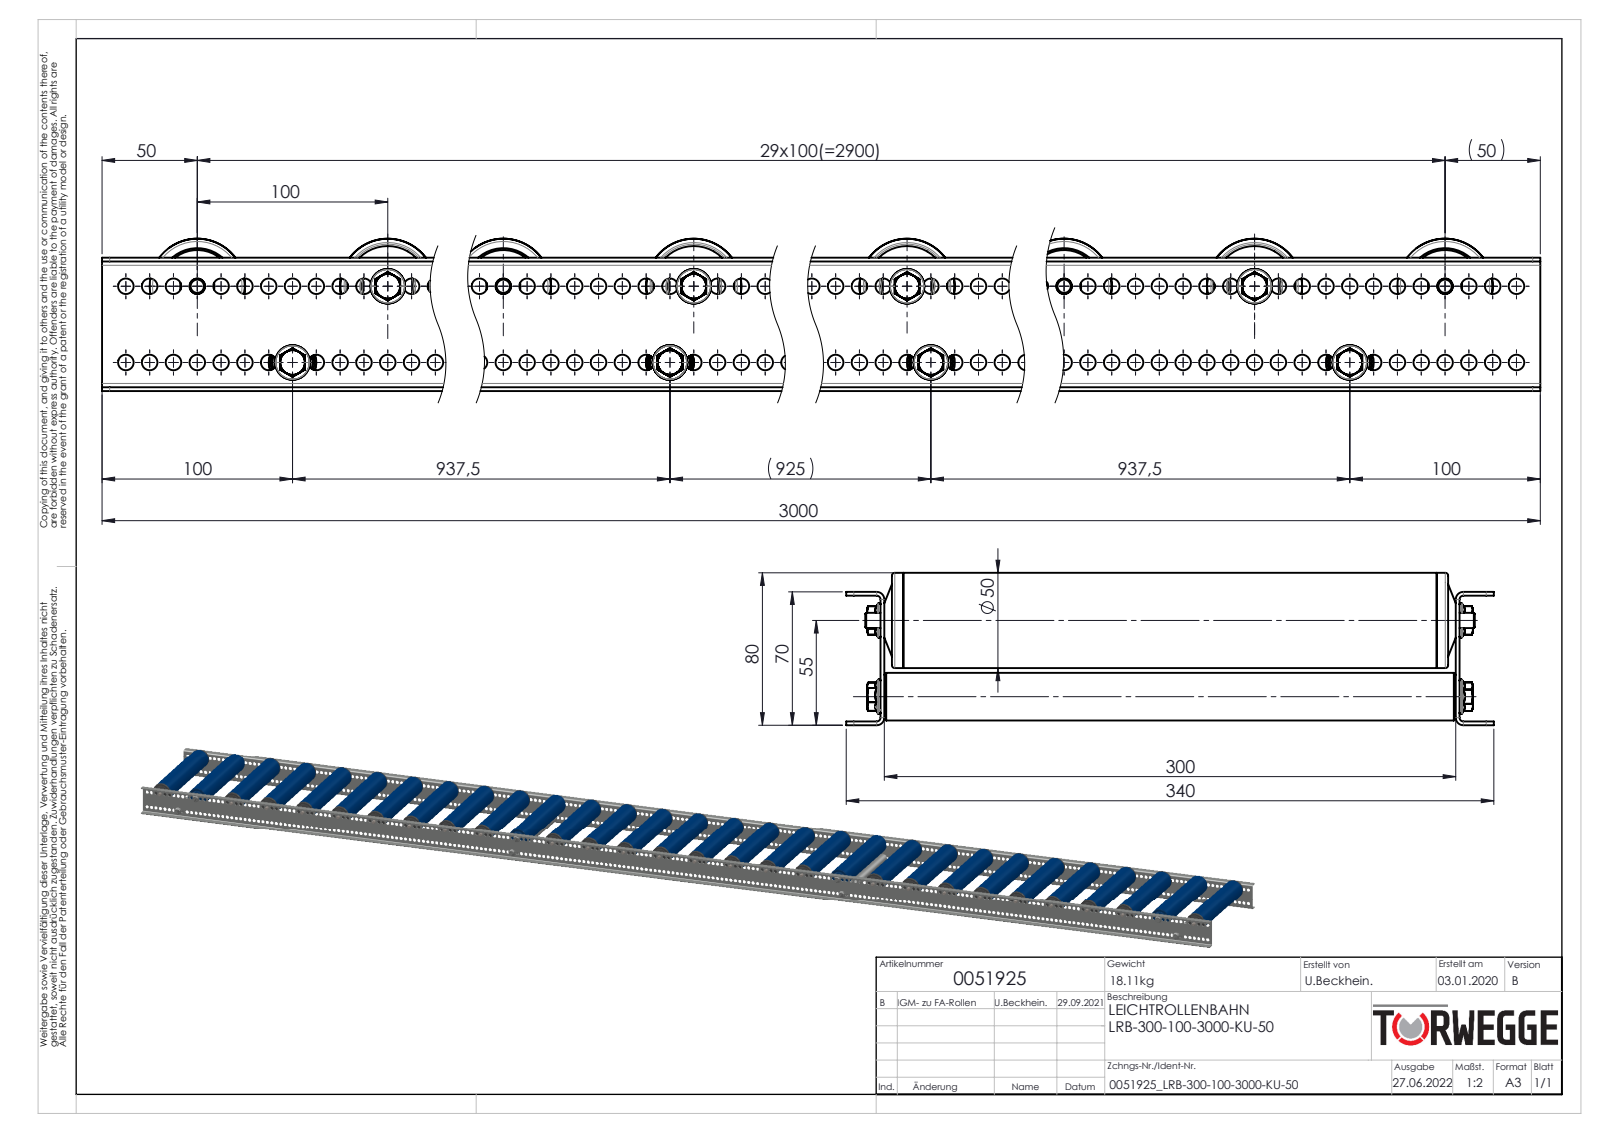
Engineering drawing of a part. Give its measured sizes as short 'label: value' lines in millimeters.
name: KUT100-50x2,8-KB-A12-IGM8-EL=KFG_S100913_KUT100-50x2,8-KB-A12-IGM8-EL=300; 0039778-Achse-ST-Ø08-KFG_AL320-G; Druckfeder_1,2x10x30; Sicherungsring_DIN471_8x0.8_Circlip DIN 471 - 8 x 0.8 (+8 more)
written by: SolidWorks 2020 (AUTOMOTIVE_DESIGN)
unit: mm
bodies: 529 solids, 10474 faces (2574 planar, 4860 cylindrical, 3040 other)
size: 3000 × 340 × 80
volume: 7 085 000 mm³; area: 5 481 000 mm²
holes: 478× ⌀8.2, 26× ⌀7.6, 26× ⌀8, 26× ⌀25, 26× ⌀30, 26× ⌀35, 26× ⌀39.4, 26× ⌀40, 8× ⌀6.8, 4× ⌀12, 4× ⌀12.1, 4× ⌀16
bosses: 30× ⌀50, 26× ⌀44.4, 26× ⌀38, 26× ⌀36, 26× ⌀33, 26× ⌀22, 26× ⌀21, 8× ⌀25
rounds: 52× R0.6, 52× R0.75, 52× R2.45, 26× R4.87, 26× R7, 16× R2.5, 8× R4, 4× R2
face distances: 2, 302, 68, 300, 304, 70, 66, 292, 6, 12
hole spacings: 12.5, 25, 37.5, 50, 62.5, 75, 87.5, 100
